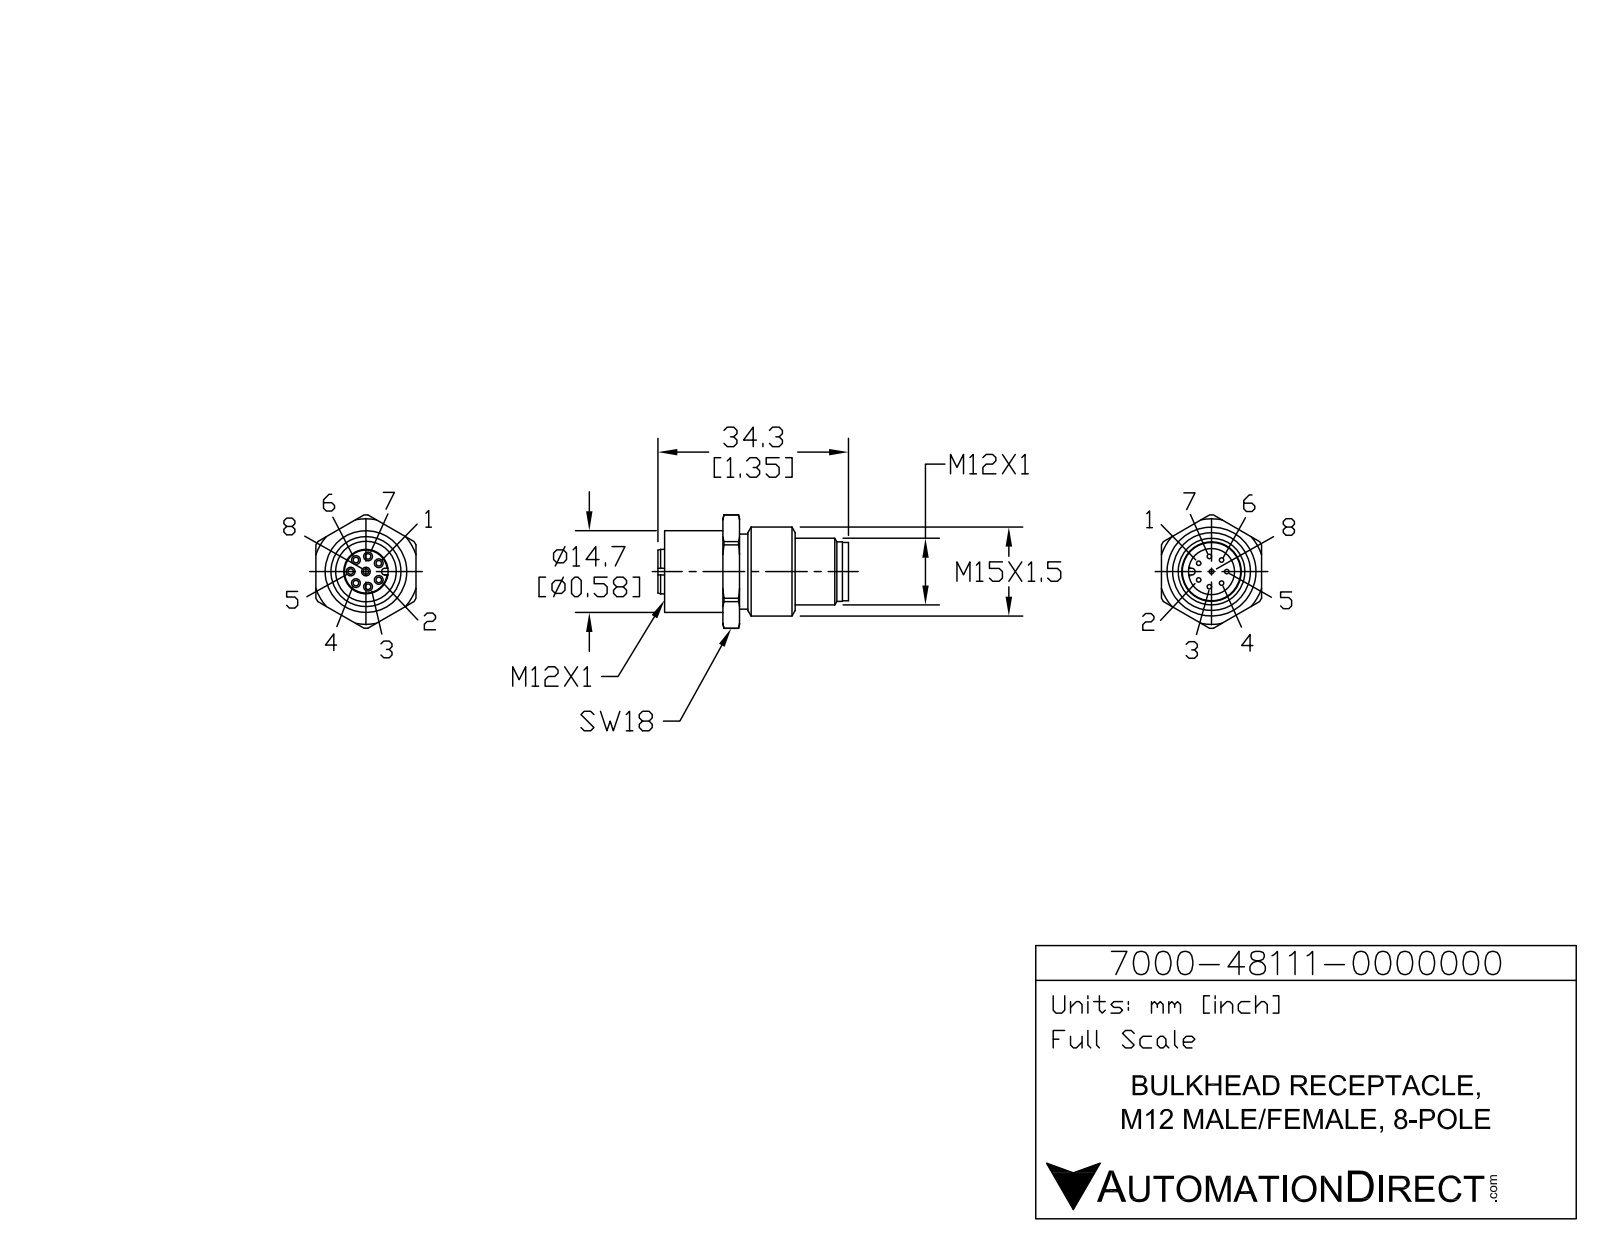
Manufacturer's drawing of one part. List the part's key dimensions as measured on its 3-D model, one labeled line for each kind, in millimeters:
Part name (STEP PRODUCT): 7000-48111--0000000
STEP written by: SolidWorks 2015 (AUTOMOTIVE_DESIGN)
Units: millimetres
Bodies: 1 solid, 161 faces (38 planar, 64 cylindrical, 59 other)
Overall size (bounding box): 34.3 × 20.4 × 18
Volume: 4 739 mm³ · Surface area: 3 250 mm²
Round holes (diameter × count): ⌀1 ×8, ⌀8.3 ×1, ⌀10.9 ×1
Round bosses / shafts (diameter × count): ⌀0.8 ×8, ⌀16 ×1, ⌀14.7 ×1, ⌀13.5 ×1, ⌀12 ×1, ⌀10.7 ×1, ⌀10.5 ×1, ⌀8 ×1
Partial cylindrical surfaces — rounded edges, fillets, slot ends (radius × count): R0.2 ×2, R0.6 ×2, R10.2 ×1
Main face-to-face distances: 3, 18, 10, 24.2, 7.8, 10.5, 13.5, 13.7, 10.7, 2.7
Hole centre spacings: 2.75, 4.15, 2.28, 2.27, 4.64, 5.28, 5.44, 2.29
